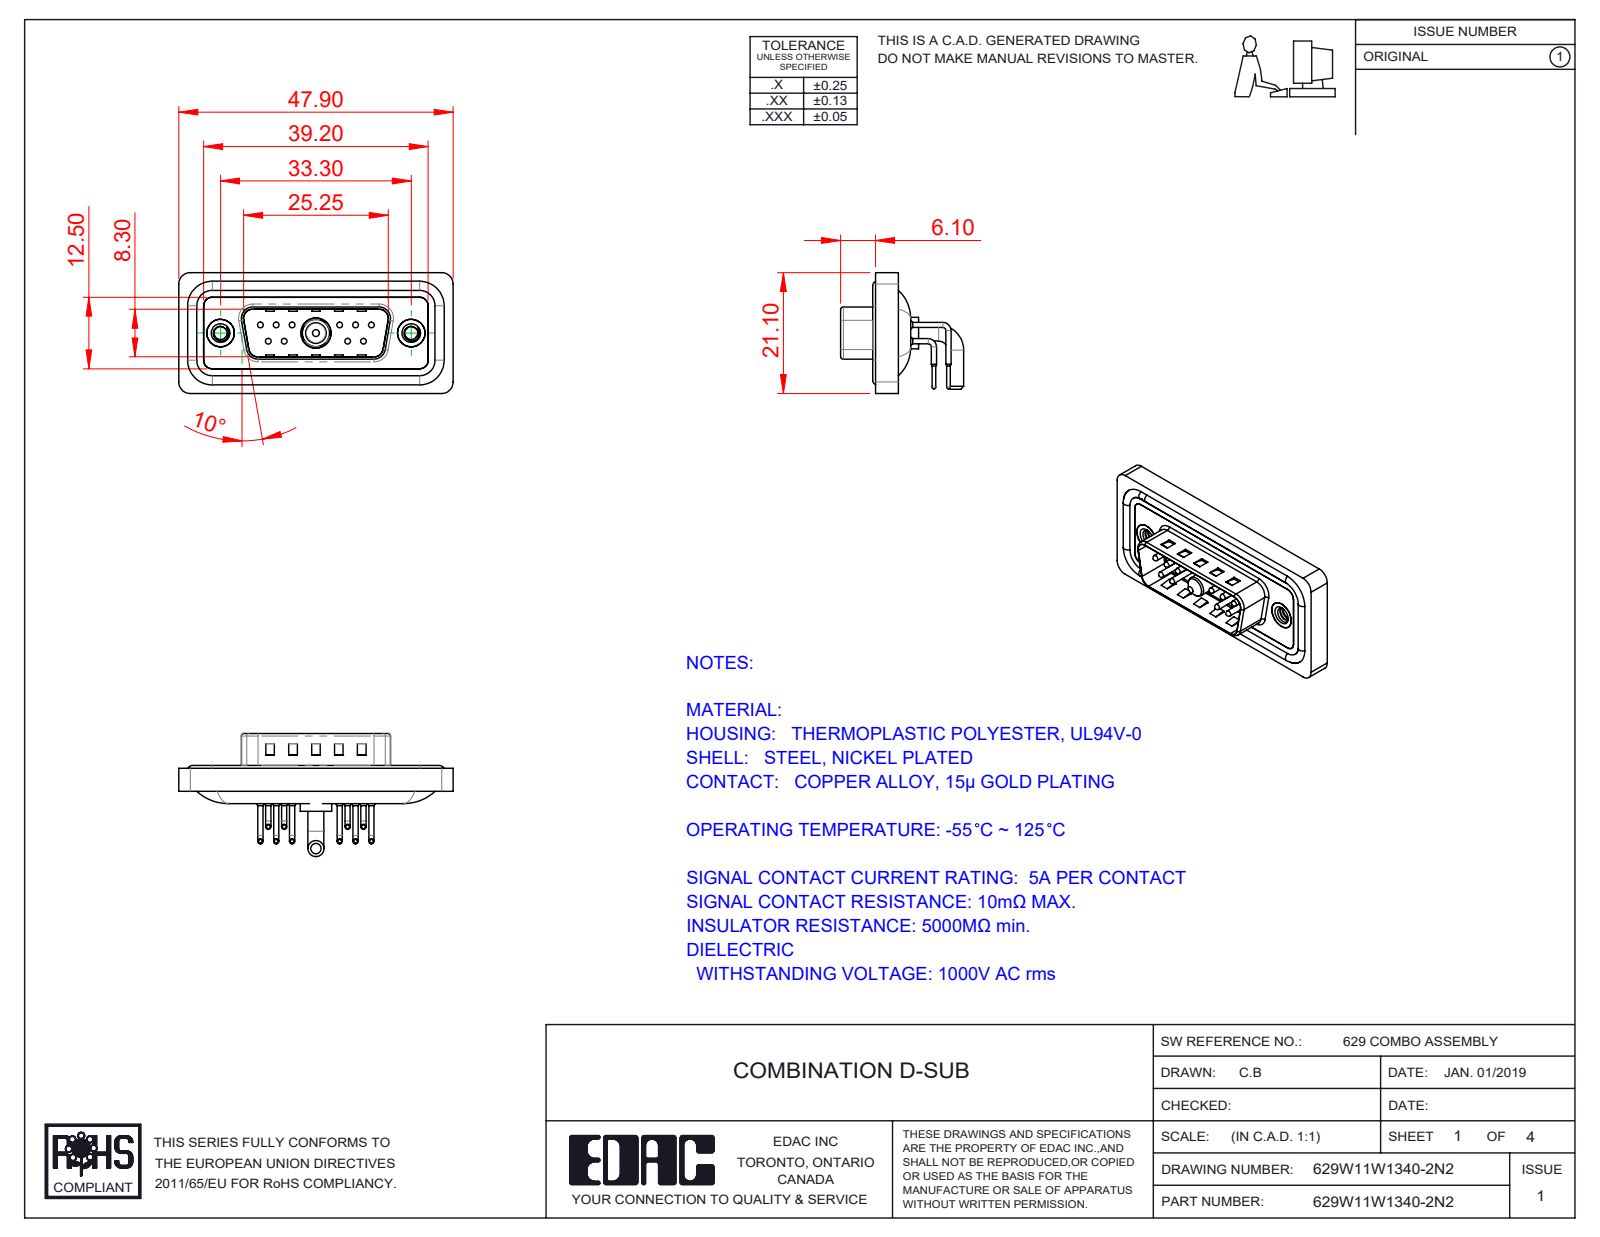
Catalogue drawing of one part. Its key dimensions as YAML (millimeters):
part_name: "629Combo Housing_11W1; 629Combo Contact Row 1; 629Combo Threaded Rivet_2; 629Combo Shell Rear_15 Contacts (+5 more)"
step_written_by: "SolidWorks 2023 (CONFIG_CONTROL_DESIGN)"
units: millimeters
bodies: {solids: 19, faces: 1603, planar: 836, cylindrical: 569, other: 198}
overall_size: [47.9, 21.5, 21.1]
volume: 5600
surface_area: 9280
round_holes:
  - {diameter: 0.75, count: 10}
  - {diameter: 1.6, count: 10}
  - {diameter: 2, count: 10}
  - {diameter: 2.26, count: 2}
  - {diameter: 4, count: 2}
  - {diameter: 4.8, count: 2}
  - {diameter: 5, count: 2}
  - {diameter: 4.85, count: 1}
  - {diameter: 5.3, count: 1}
round_bosses_or_shafts:
  - {diameter: 0.9, count: 20}
  - {diameter: 1.5, count: 10}
  - {diameter: 1, count: 10}
  - {diameter: 0.65, count: 10}
  - {diameter: 1.6, count: 4}
  - {diameter: 4.9, count: 2}
  - {diameter: 2.8, count: 2}
  - {diameter: 5.5, count: 1}
partial_cylinders:
  - {radius: 2, count: 20}
  - {radius: 1.5, count: 18}
  - {radius: 1.01, count: 10}
  - {radius: 0.5, count: 8}
  - {radius: 1.6, count: 8}
  - {radius: 1, count: 7}
  - {radius: 0.25, count: 4}
  - {radius: 0.6, count: 4}
face_to_face_distances: [0.4, 2.9, 0.8, 1.1, 2.1, 1.6, 2.5, 4.1, 4.5, 3.1]
hole_center_spacings: [3.16, 2.77, 13.85, 11.08, 16.62, 5.03, 5.04, 5.54]
